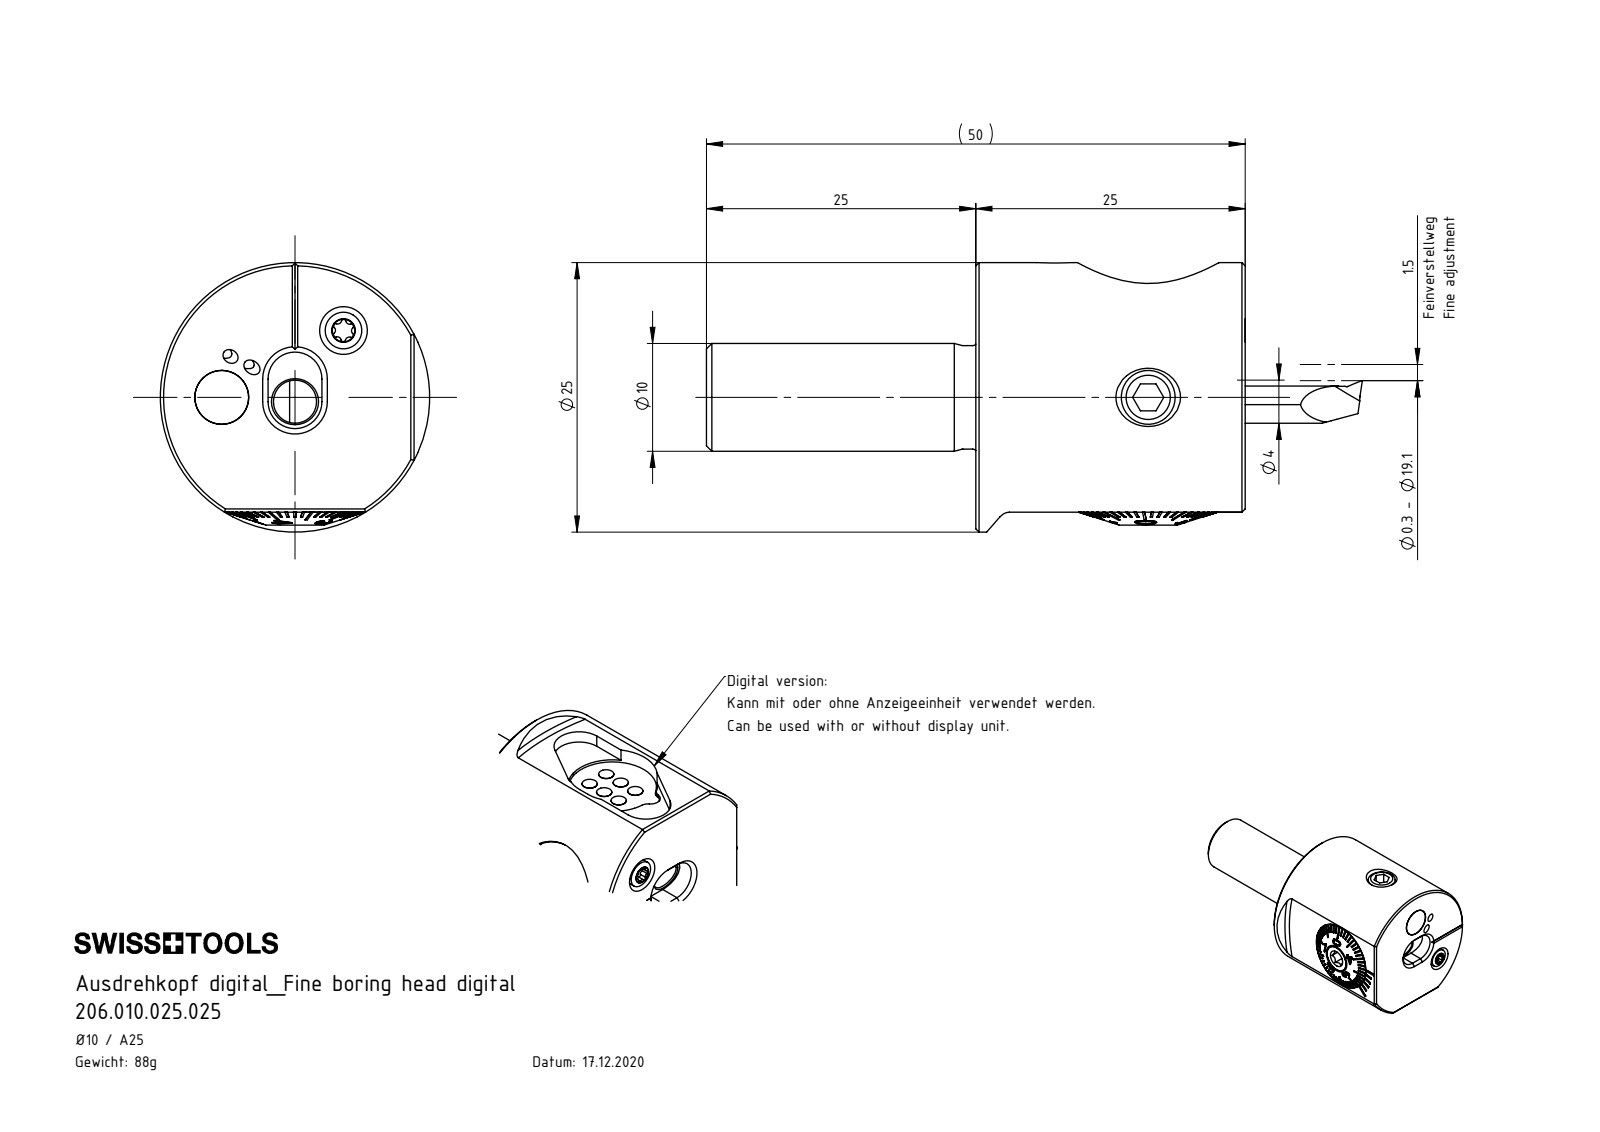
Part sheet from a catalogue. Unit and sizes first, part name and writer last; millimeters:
Units: millimetres
Overall size (bounding box): 61 × 25 × 25
Round holes (diameter × count): ⌀3.3 ×4, ⌀5 ×4, ⌀2 ×2, ⌀0.7 ×1, ⌀1 ×1, ⌀2.4 ×1, ⌀2.7 ×1, ⌀3 ×1, ⌀4 ×1, ⌀4.2 ×1, ⌀6.75 ×1, ⌀7.3 ×1
Round bosses / shafts (diameter × count): ⌀1.9 ×6, ⌀4 ×3, ⌀4.95 ×2, ⌀25 ×1, ⌀13 ×1, ⌀12.98 ×1, ⌀12.85 ×1, ⌀10.65 ×1
Partial cylindrical surfaces — rounded edges, fillets, slot ends (radius × count): R0.21 ×6, R0.36 ×5, R0.2 ×4, R2.2 ×4, R0.5 ×3, R1.1 ×3, R1.2 ×3, R1.6 ×3
Main face-to-face distances: 25, 3.9, 1.5, 0.8, 3.1, 1.6, 3.8, 2.3, 3, 1.35
Hole centre spacings: 3.5, 5.48, 9.25, 0.4, 0.68, 2.6, 2.61, 6.25
Volume: 11 822 mm³ · Surface area: 10 029 mm²
Bodies: 18 solids, 835 faces (364 planar, 180 cylindrical, 291 other)
Part name (STEP PRODUCT): Mini_Schaft_4; ISO 4026 - M5 x 4_PreviewCfg; A25-BG3.005.018_A; A25-BG1.DA2.013 (+8 more)
STEP written by: SolidWorks 2017 (CONFIG_CONTROL_DESIGN)
